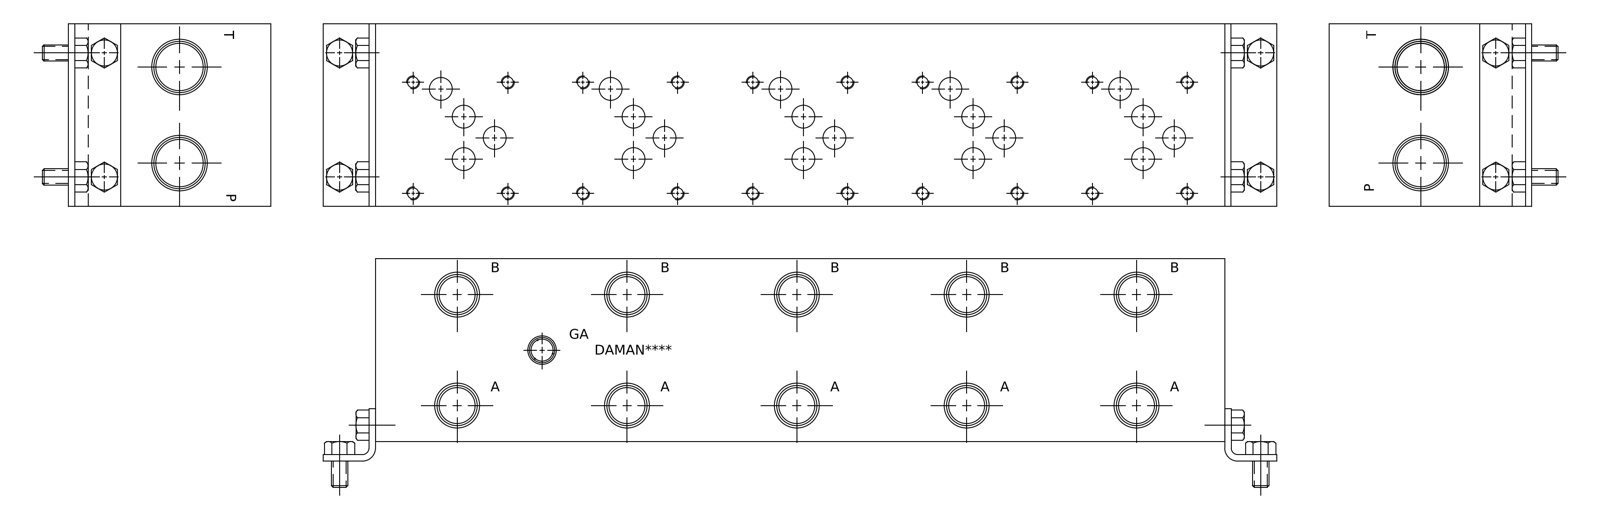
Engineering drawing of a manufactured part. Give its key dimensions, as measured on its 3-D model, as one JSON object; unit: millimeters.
{"part_name": "Part_AD05P053P_3D", "step_written_by": "Autodesk Inventor 2020 (AUTOMOTIVE_DESIGN)", "units": "millimeters", "bodies": {"solids": 1, "faces": 803, "planar": 445, "cylindrical": 98, "other": 260}, "overall_size": [412.75, 88.9, 88.9], "volume_mm3": 3133000, "surface_area_mm2": 193160, "round_holes": [[5.11, 20], [6.35, 20], [11.13, 20], [17.48, 10], [21.59, 10], [6.53, 2], [7.92, 2], [23.01, 2], [26.92, 2], [10.72, 1], [13.87, 1]], "face_to_face_distances": [88.9, 412.75, 15.37, 73.53, 15.85, 396.9, 381.05, 15.33, 88.86, 69.85], "hole_center_spacings": [82.55, 165.1, 98.63, 247.65, 46.05, 53.98, 70.95, 98.61]}
